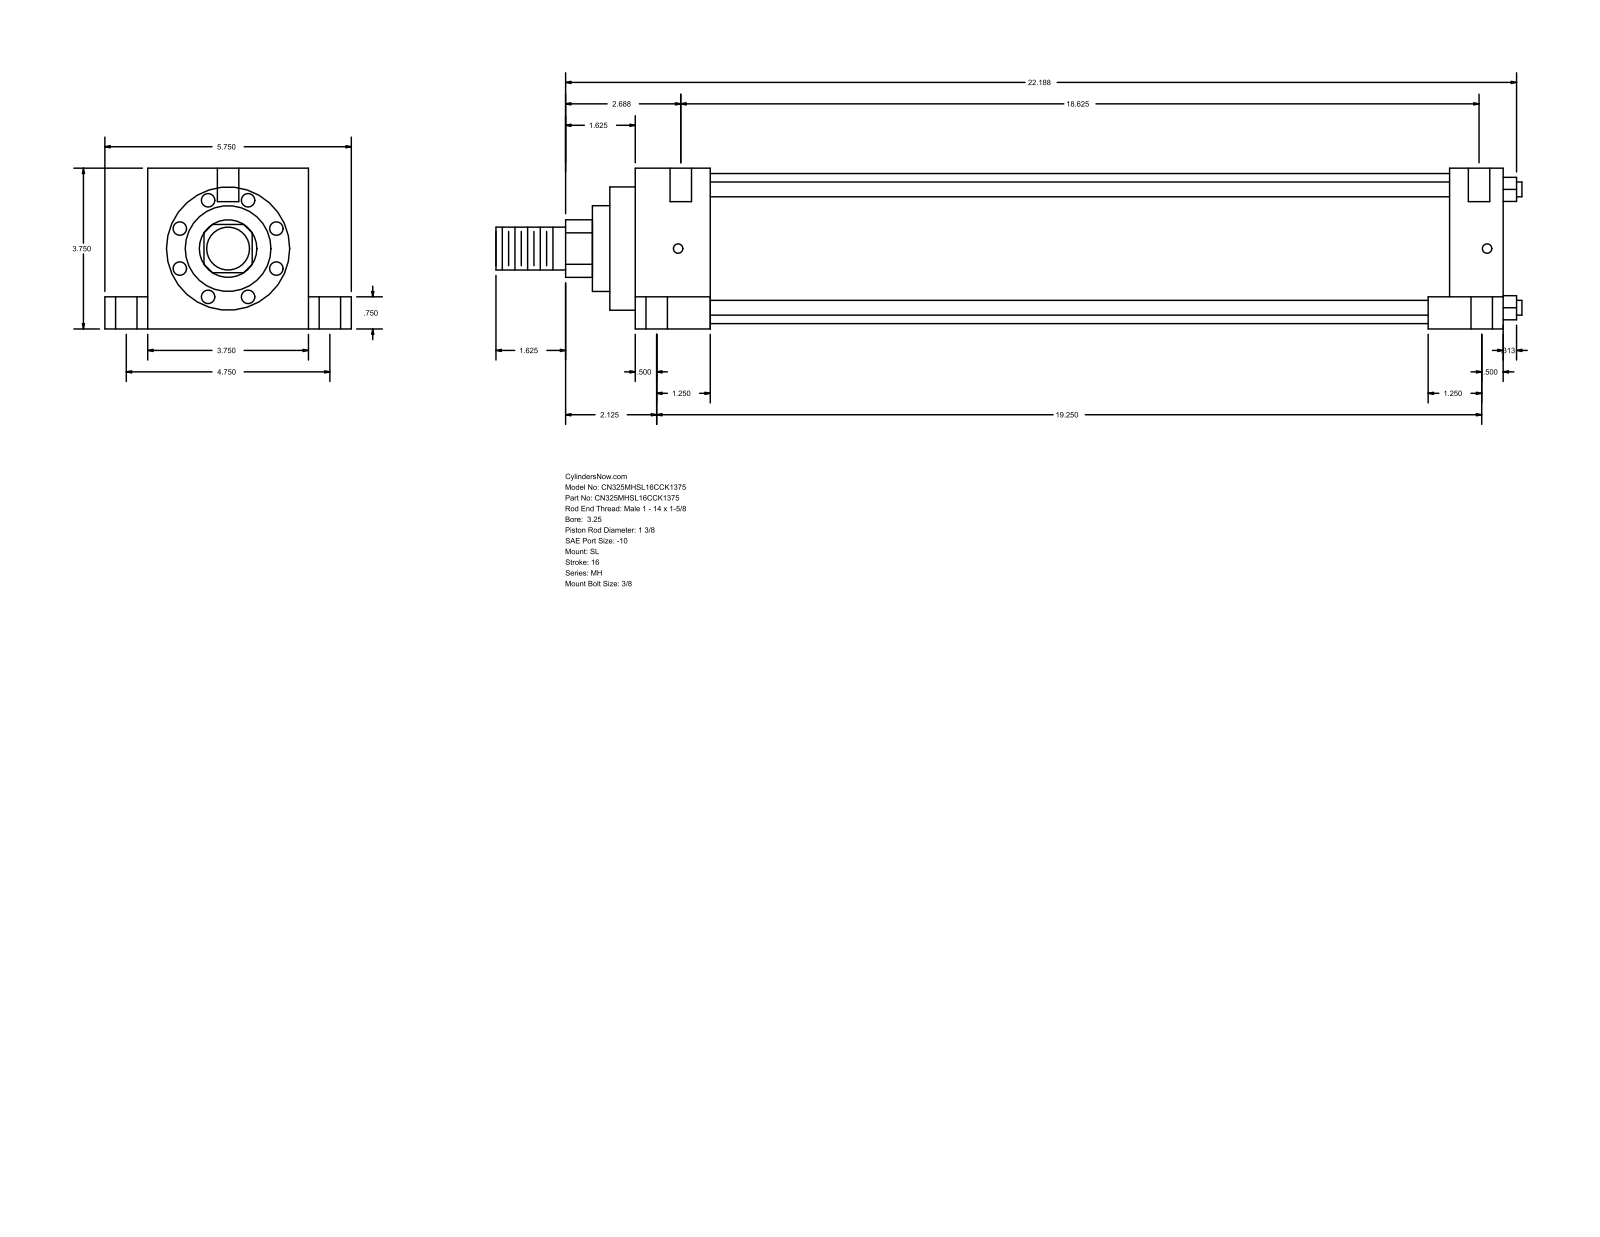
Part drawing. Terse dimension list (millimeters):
name: MH_SL__0325_1.375
written by: GSSL Pune (CONFIG_CONTROL_DESIGN)
unit: mm
bodies: 0 solids, 110 faces (77 planar, 33 cylindrical, 0 other)
size: 608.01 × 146.05 × 95.25
holes: 6× ⌀12.7, 4× ⌀5.56, 4× ⌀19.05
bosses: 4× ⌀8.76, 1× ⌀88.9, 1× ⌀73.03, 1× ⌀50.8, 1× ⌀34.92, 1× ⌀25.4
rounds: 1× R17.06
face distances: 95.24, 514.35, 44.45, 469.9, 25.41, 120.65, 19.05, 76.19, 482.61, 438.16
hole spacings: 60.35, 60.41, 61.65, 62, 120.66, 478.48, 479.43, 480.06
